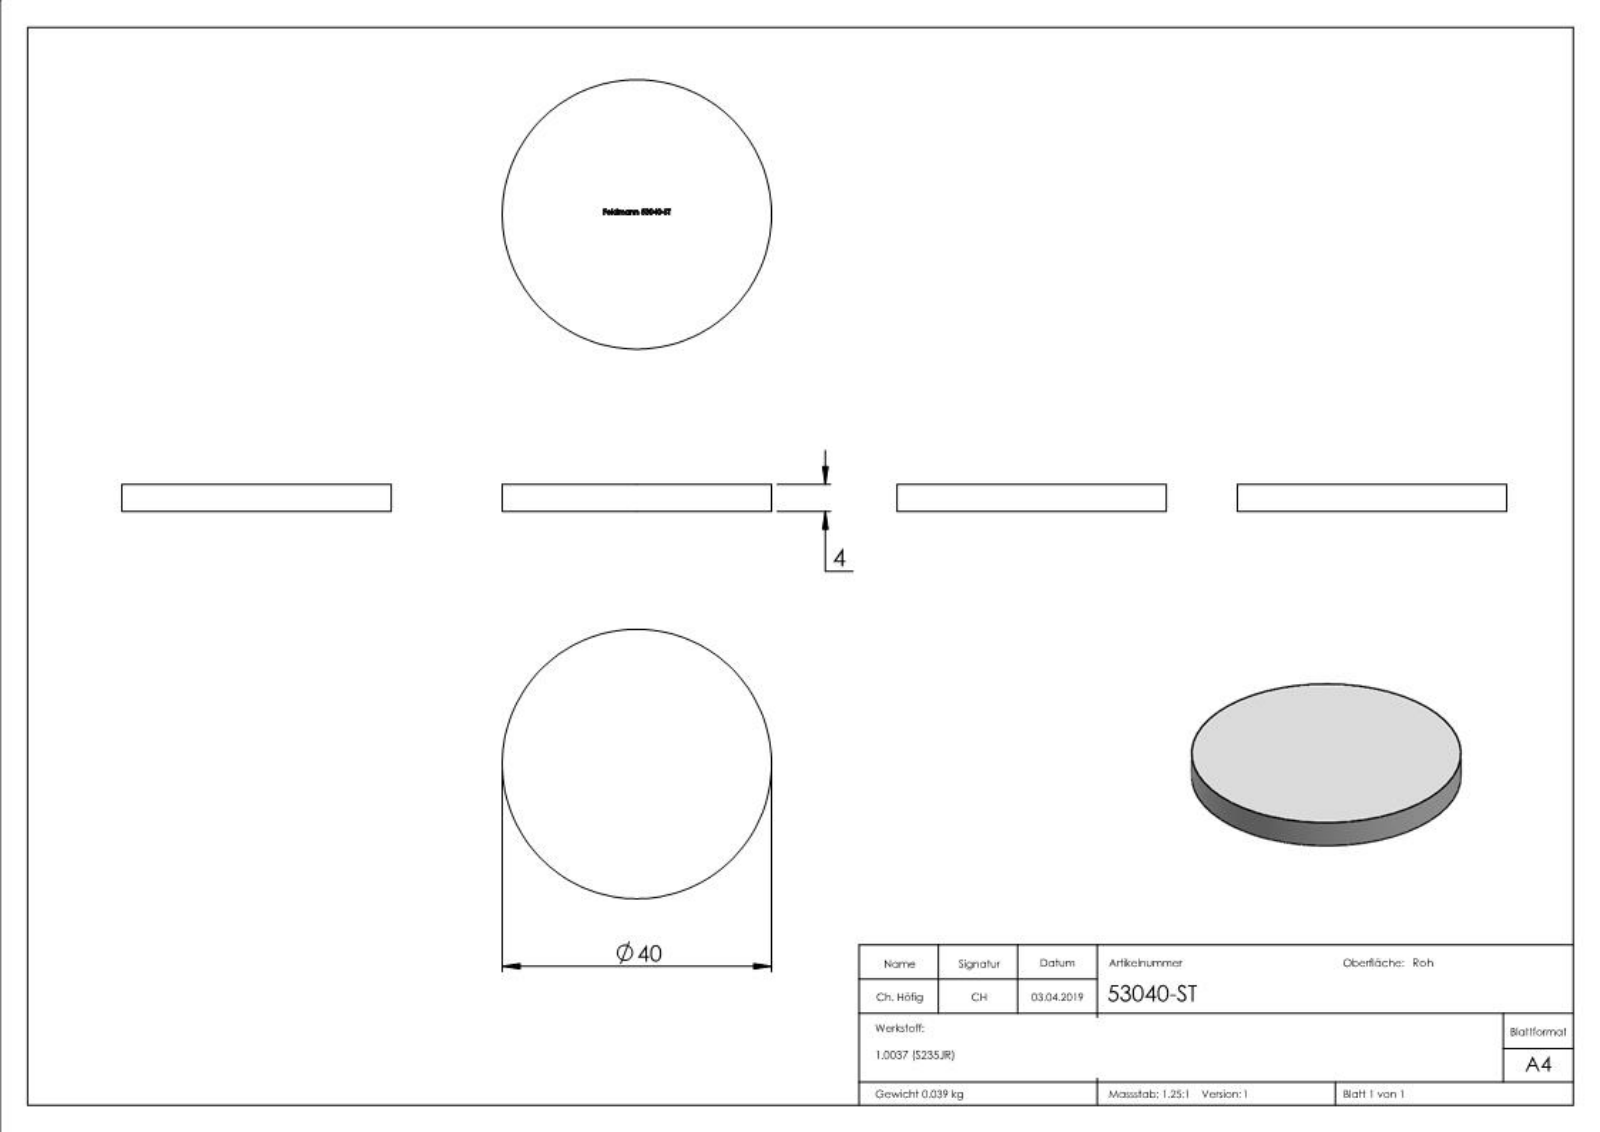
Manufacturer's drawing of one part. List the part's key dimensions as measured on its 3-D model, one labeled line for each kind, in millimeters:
Part name (STEP PRODUCT): 53040-ST
STEP written by: SolidWorks 2015 (CONFIG_CONTROL_DESIGN)
Units: millimetres
Bodies: 1 solid, 219 faces (114 planar, 2 cylindrical, 103 other)
Overall size (bounding box): 40 × 40 × 4
Volume: 5 026 mm³ · Surface area: 3 021 mm²
Round bosses / shafts (diameter × count): ⌀40 ×1
Main face-to-face distances: 4, 3.9, 0.44, 0.79, 0.99, 1.78, 1.21, 8.49, 9.7, 0.75
